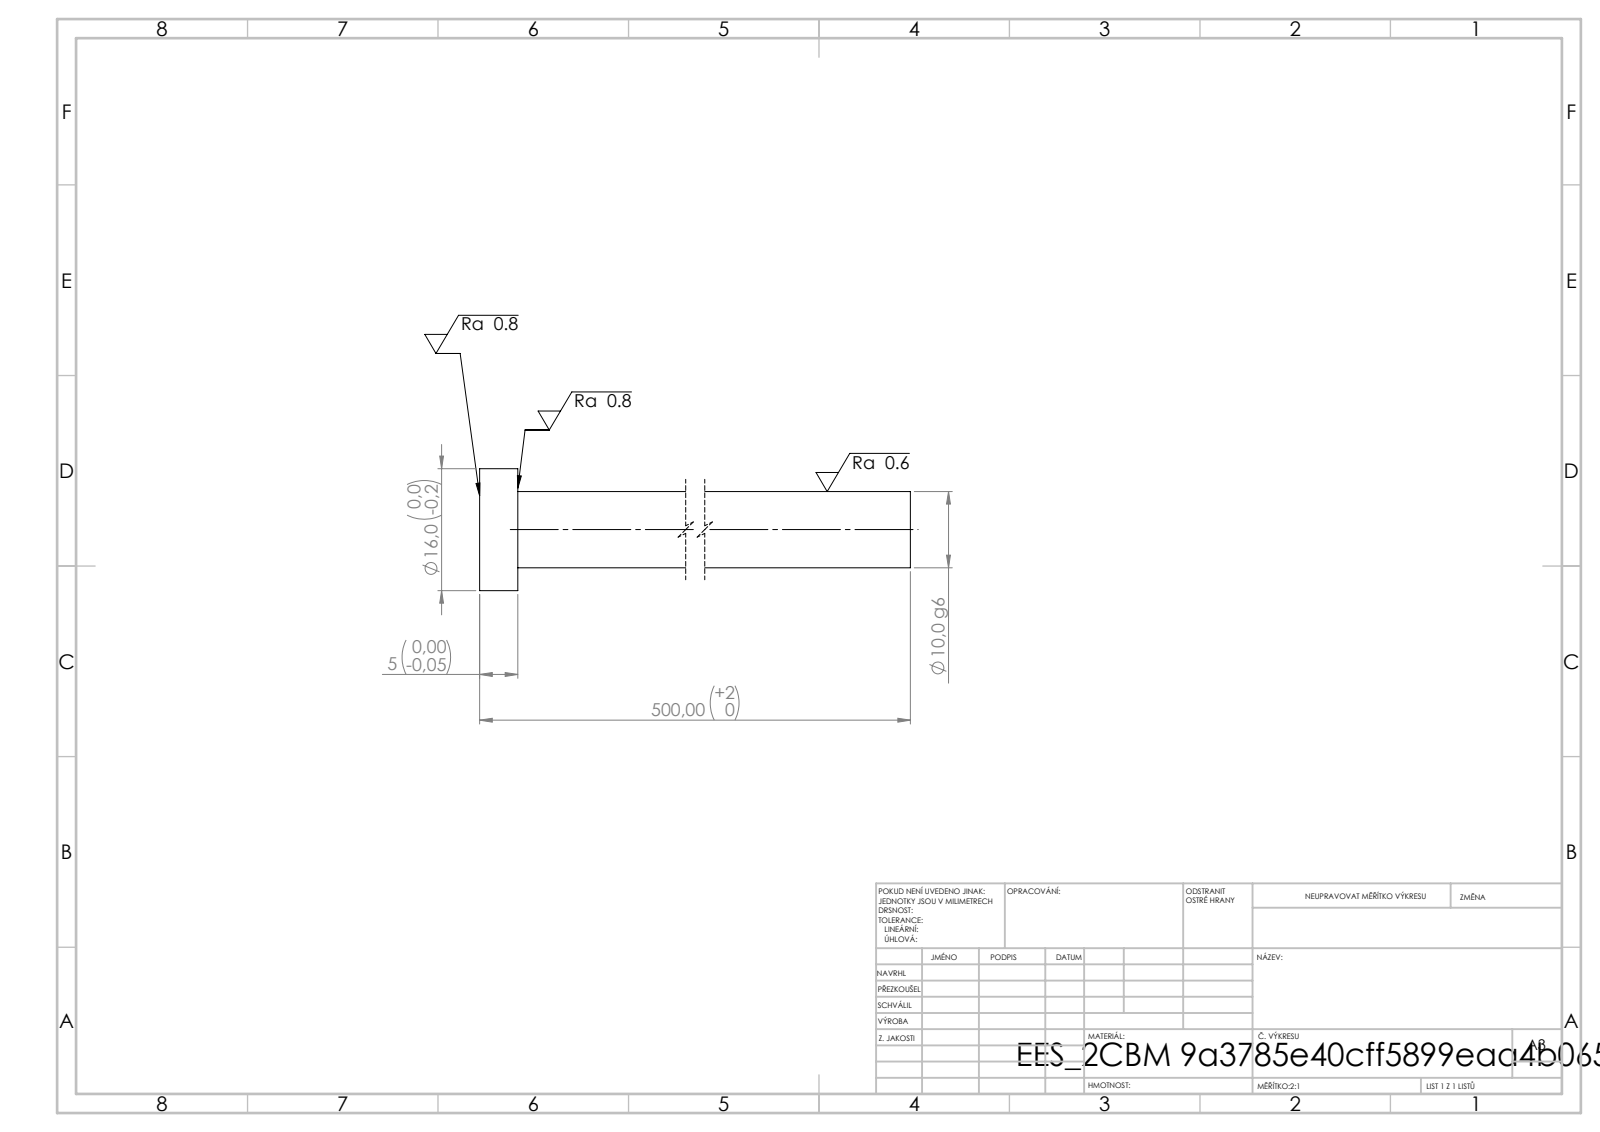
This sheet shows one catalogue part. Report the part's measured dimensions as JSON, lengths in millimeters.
{"step_written_by": "SolidWorks 2019 (CONFIG_CONTROL_DESIGN)", "units": "millimeters", "bodies": {"solids": 1, "faces": 7, "planar": 3, "cylindrical": 4, "other": 0}, "overall_size": [500, 16, 16], "volume_mm3": 39883, "surface_area_mm2": 16204, "round_bosses_or_shafts": [[16, 1], [10, 1]], "face_to_face_distances": [5, 500, 495]}
